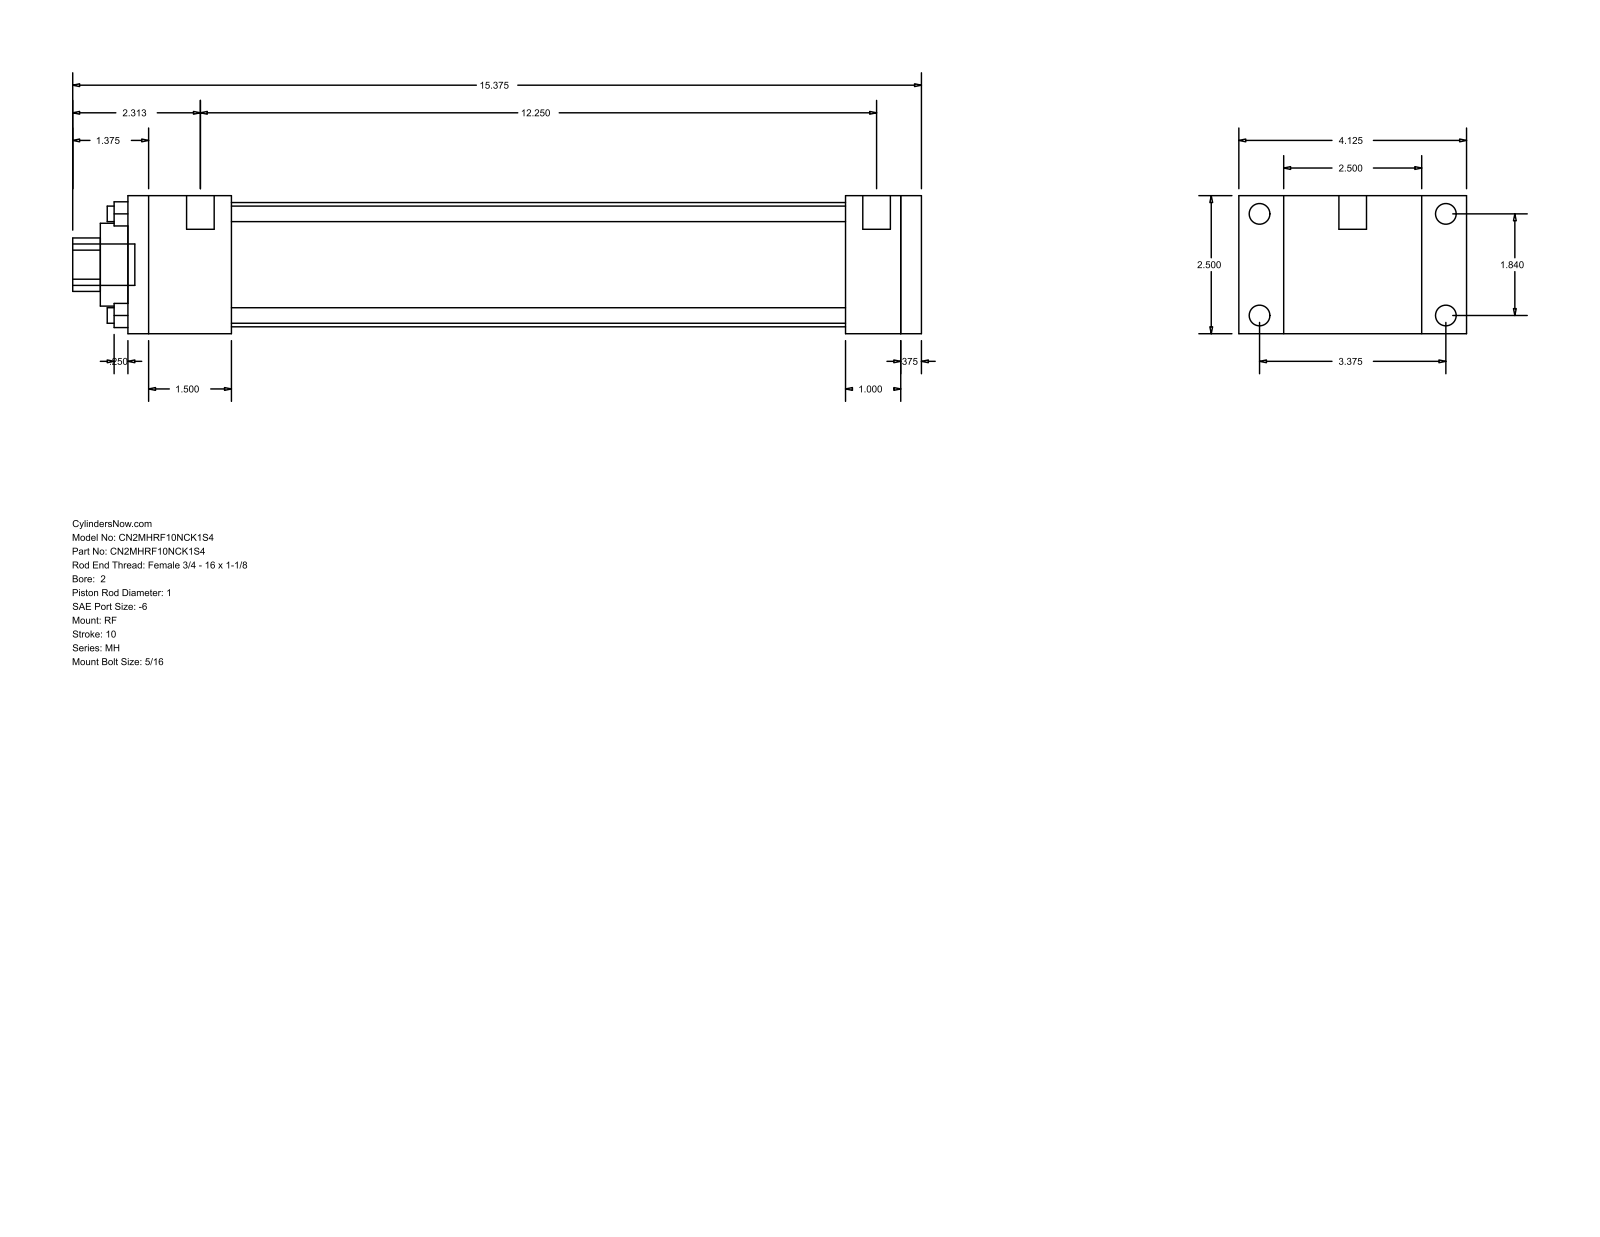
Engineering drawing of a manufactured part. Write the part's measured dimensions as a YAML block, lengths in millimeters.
part_name: "MH_RF__0200_1"
step_written_by: "GSSL Pune (CONFIG_CONTROL_DESIGN)"
units: millimeters
bodies: {solids: 0, faces: 92, planar: 64, cylindrical: 28, other: 0}
overall_size: [390.52, 104.78, 63.5]
round_holes:
  - {diameter: 7.14, count: 4}
  - {diameter: 25.4, count: 1}
  - {diameter: 38.1, count: 1}
  - {diameter: 57.15, count: 1}
round_bosses_or_shafts:
  - {diameter: 9.53, count: 4}
  - {diameter: 5.56, count: 4}
  - {diameter: 12.7, count: 2}
  - {diameter: 19.05, count: 1}
partial_cylinders:
  - {radius: 12.29, count: 1}
face_to_face_distances: [63.5, 9.52, 365.12, 355.6, 20.64, 25.4, 47.63, 330.2, 282.57, 307.97]
hole_center_spacings: [33.05, 46.74, 66.1]
